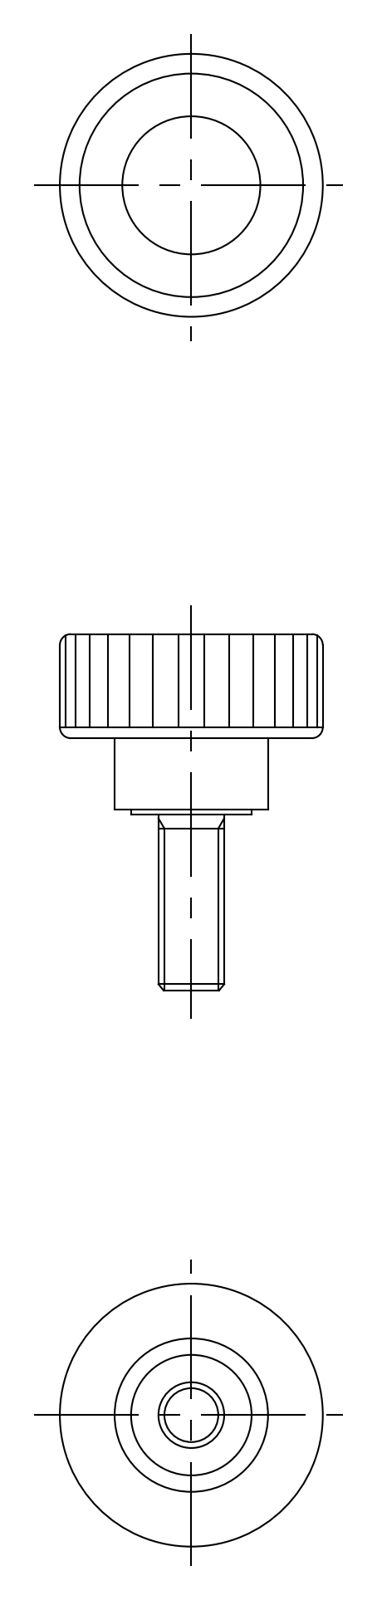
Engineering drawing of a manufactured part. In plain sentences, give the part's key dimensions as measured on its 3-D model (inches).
The part is named "screw; knob; KIMS_24_M6_16_4029_36". Its 3-D file was written by "CADfix (AUTOMOTIVE_DESIGN)". It is 2 solids with 32 faces: 0 planar, 0 cylindrical and 32 other. Overall it measures 1.28 by 0.945 by 0.945 inches. Its volume is 0.212 cubic inches and its surface area 4.917 square inches.
